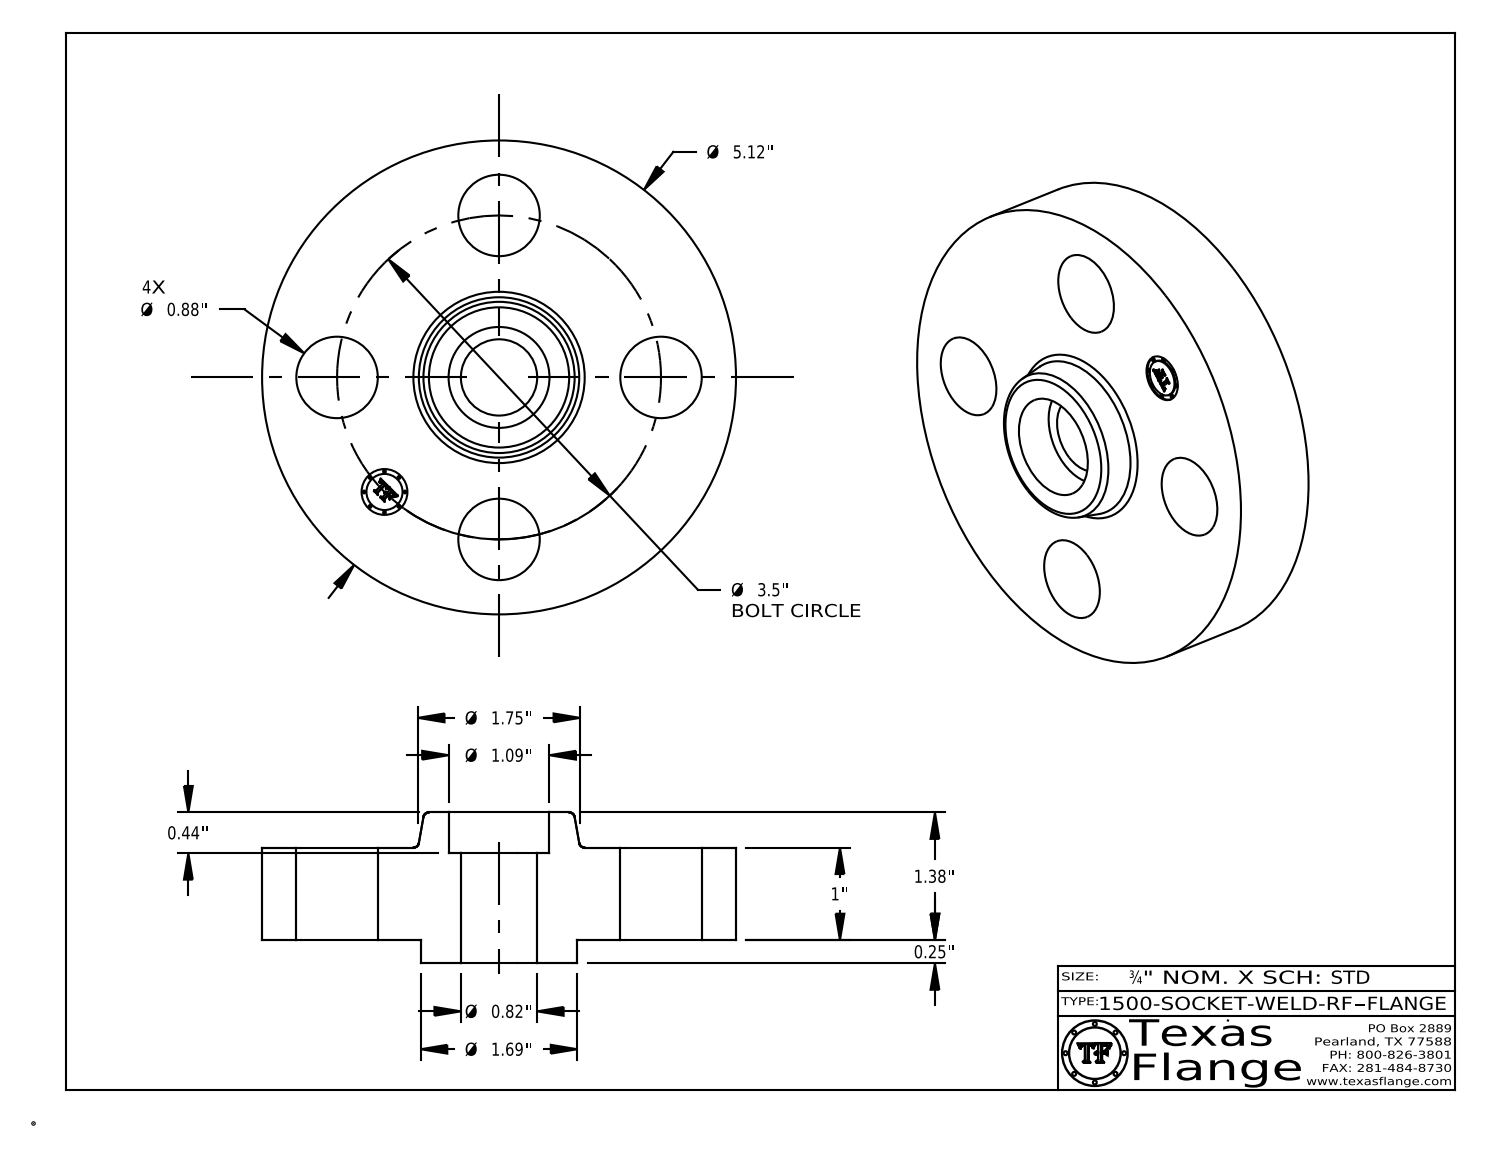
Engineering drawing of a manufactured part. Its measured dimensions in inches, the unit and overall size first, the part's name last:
Units: inches
Overall size (bounding box): 5.12 × 5.12 × 1.63
Round holes (diameter × count): ⌀0.88 ×4, ⌀0.495 ×1, ⌀0.824 ×1, ⌀1.09 ×1
Round bosses / shafts (diameter × count): ⌀0.03 ×8, ⌀5.12 ×1, ⌀1.69 ×1, ⌀0.39 ×1
Main face-to-face distances: 1, 0.25, 1.25, 1.63, 1.38, 0.38, 0.06, 1.19, 0.94, 0.44
Hole centre spacings: 1.75, 2.475, 1.339, 3.233, 3.5
Volume: 18.52 in³ · Surface area: 69.9 in²
Bodies: 1 solid, 412 faces (370 planar, 36 cylindrical, 6 other)
Part name (STEP PRODUCT): 1500-SOCKET-WELD-RF
STEP written by: CATIA V5 STEP AP214 (AUTOMOTIVE_DESIGN)
